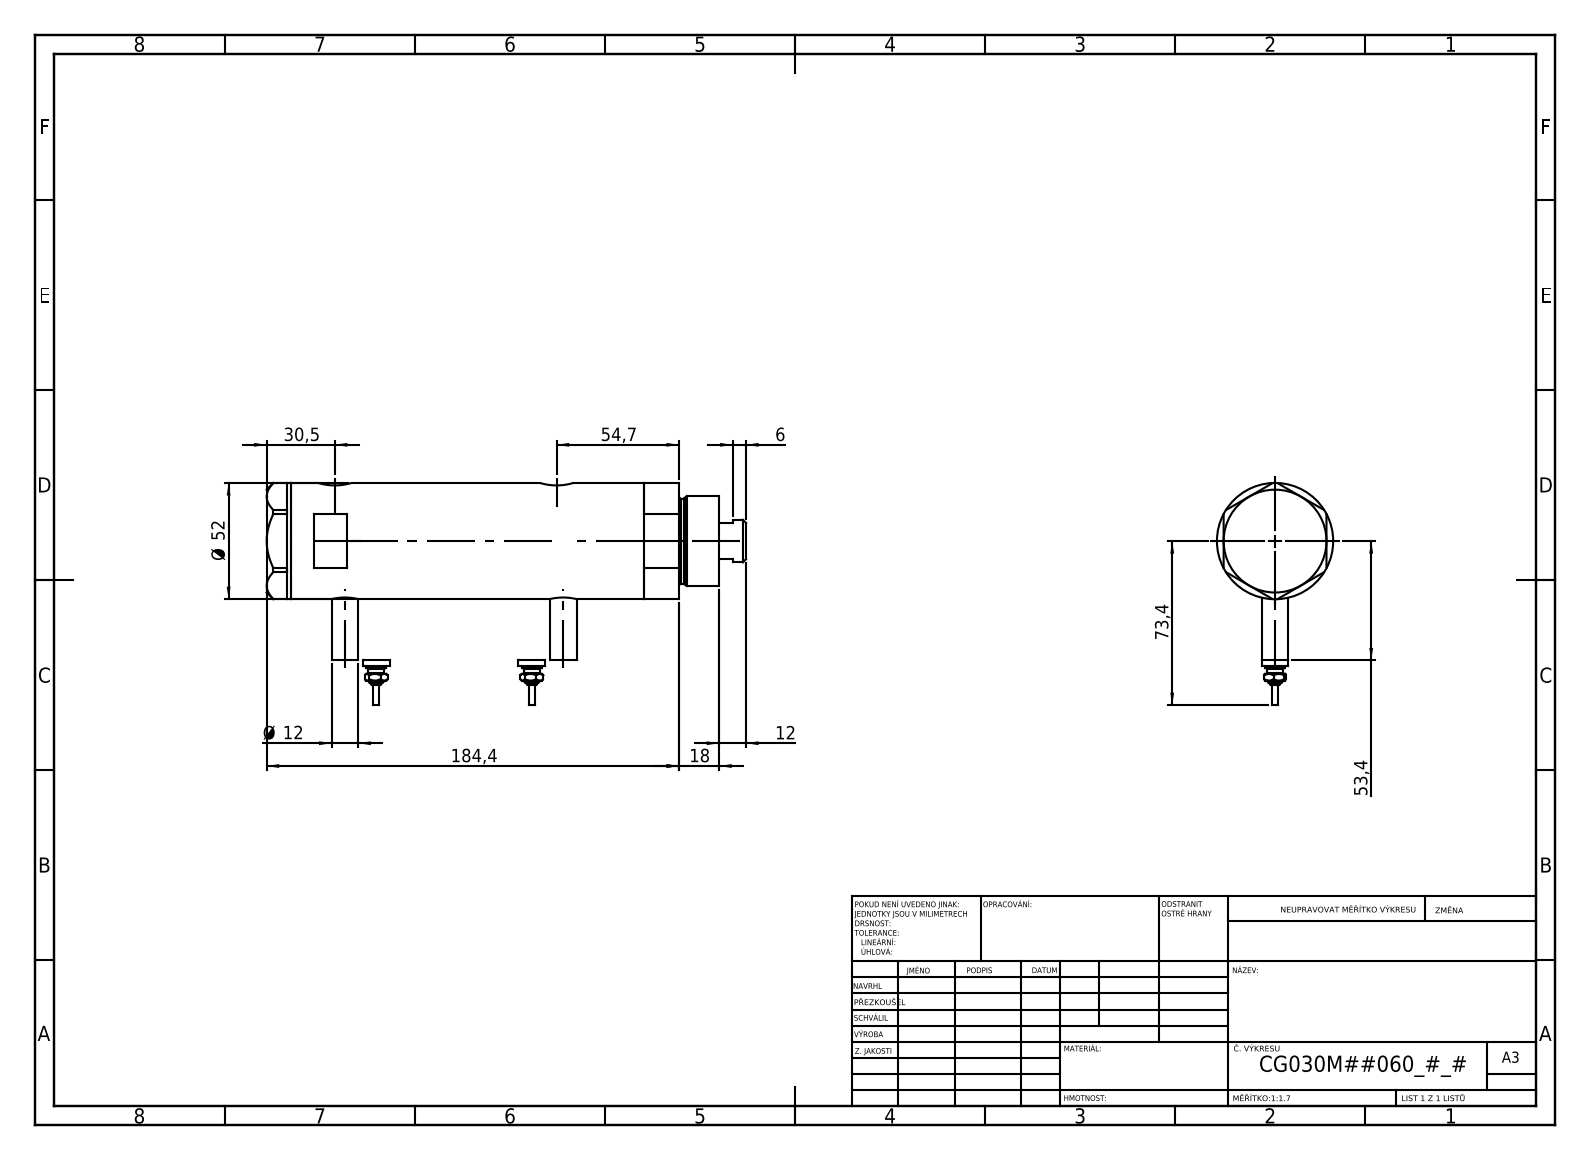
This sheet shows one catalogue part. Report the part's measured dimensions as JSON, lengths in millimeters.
{"part_name": "V270CG_MIDDLE; Switch; V270CG_FRONT; V270CG_VC (+1 more)", "step_written_by": "SolidWorks 2019 (CONFIG_CONTROL_DESIGN)", "units": "millimeters", "bodies": {"solids": 6, "faces": 226, "planar": 93, "cylindrical": 69, "other": 64}, "overall_size": [214.4, 99.4, 52], "volume_mm3": 392865, "surface_area_mm2": 89526, "round_holes": [[9.73, 2], [12.5, 2], [15, 2], [6.5, 1], [20, 1], [21.5, 1], [30, 1], [33, 1], [44, 1]], "round_bosses_or_shafts": [[12, 4], [9, 2], [7, 2], [4.5, 2], [2.5, 2], [52, 1], [40, 1], [38, 1]], "face_to_face_distances": [121.5, 23.8, 97.7, 11, 34.8, 132.5, 46, 36.4, 168.9, 157.9], "hole_center_spacings": [2.9, 4.5, 94.7, 97.6, 99.2, 102.1]}
